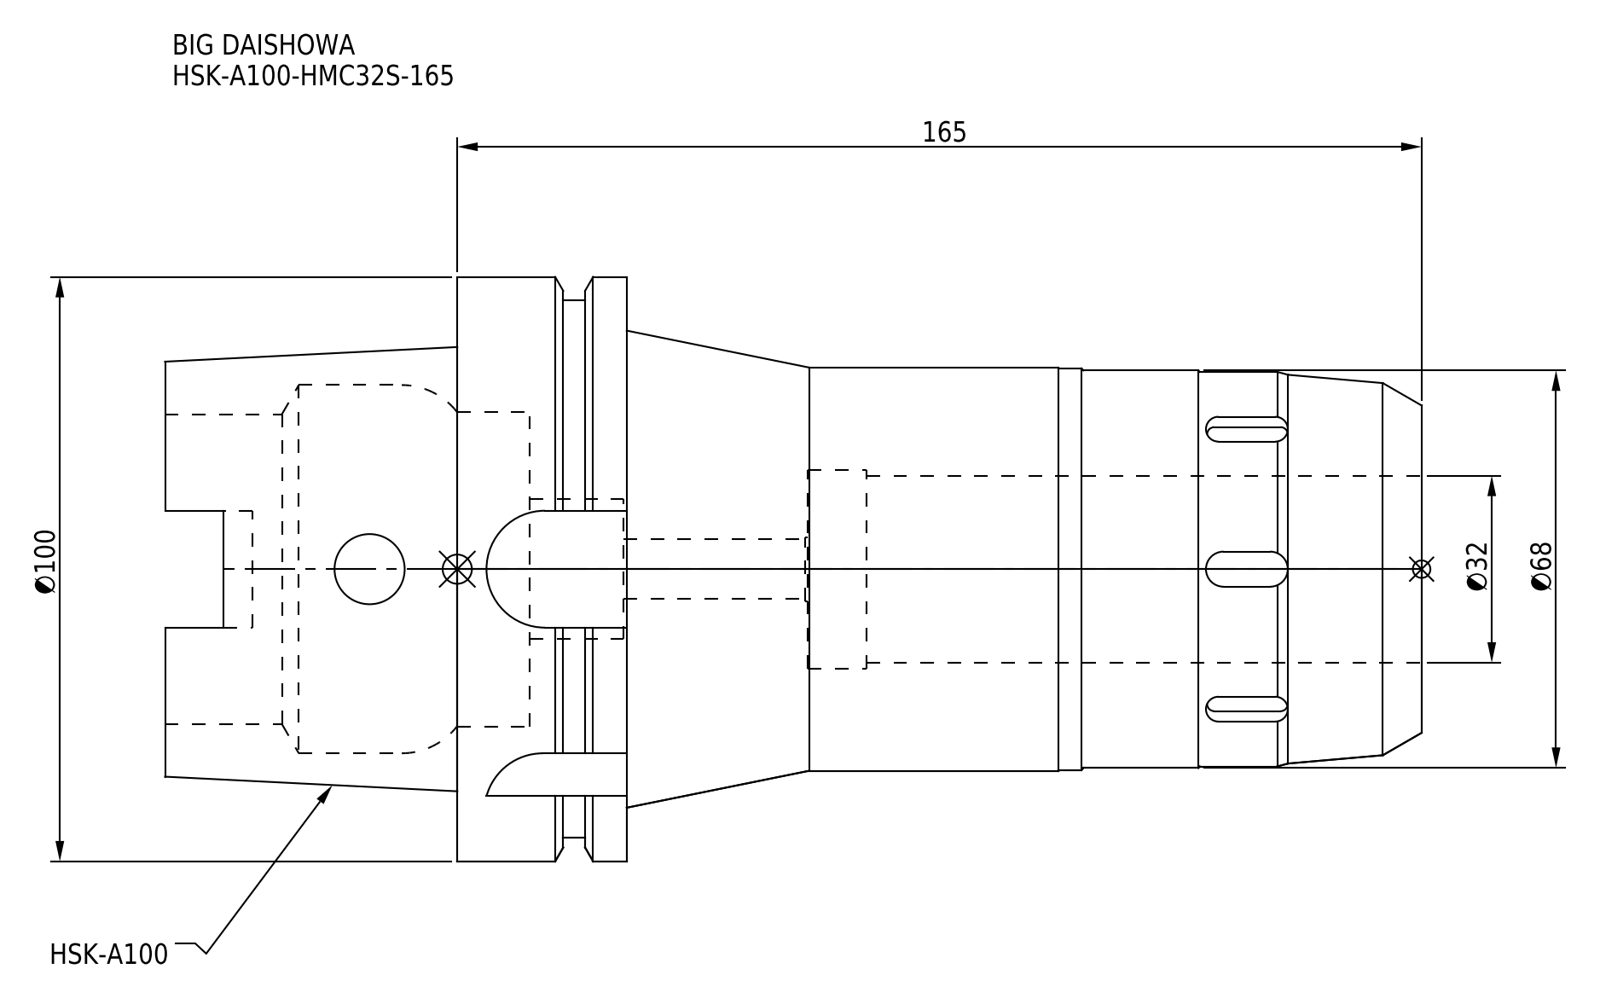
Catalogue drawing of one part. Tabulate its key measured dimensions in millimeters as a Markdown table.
| quantity | value |
| --- | --- |
| part name | HSK-A100-HMC32S-165 |
| STEP written by | CREO PARAMETRIC BY PTC INC, 2016380 (AUTOMOTIVE_DESIGN) |
| units | millimeters |
| bodies | 1 solid, 146 faces (60 planar, 62 cylindrical, 24 other) |
| overall size | 215 × 100 × 100 |
| volume | 677 710 mm³ |
| surface area | 89 633 mm² |
| round holes (diameter × count) | 10.25 × 1, 11 × 1, 12 × 1, 24 × 1, 32 × 1, 34 × 1, 53 × 1, 53.8 × 1, 63 × 1 |
| round bosses / shafts (diameter × count) | 100 × 1, 92 × 1, 69 × 1, 68.7 × 1, 68 × 1, 67.5 × 1 |
| partial cylindrical surfaces (radius × count) | 3 × 12, 4.88 × 4, 10 × 4 |
| main face-to-face distances | 29, 16.55, 12.45, 136, 152.55, 165, 215, 79, 62.45, 50 |
